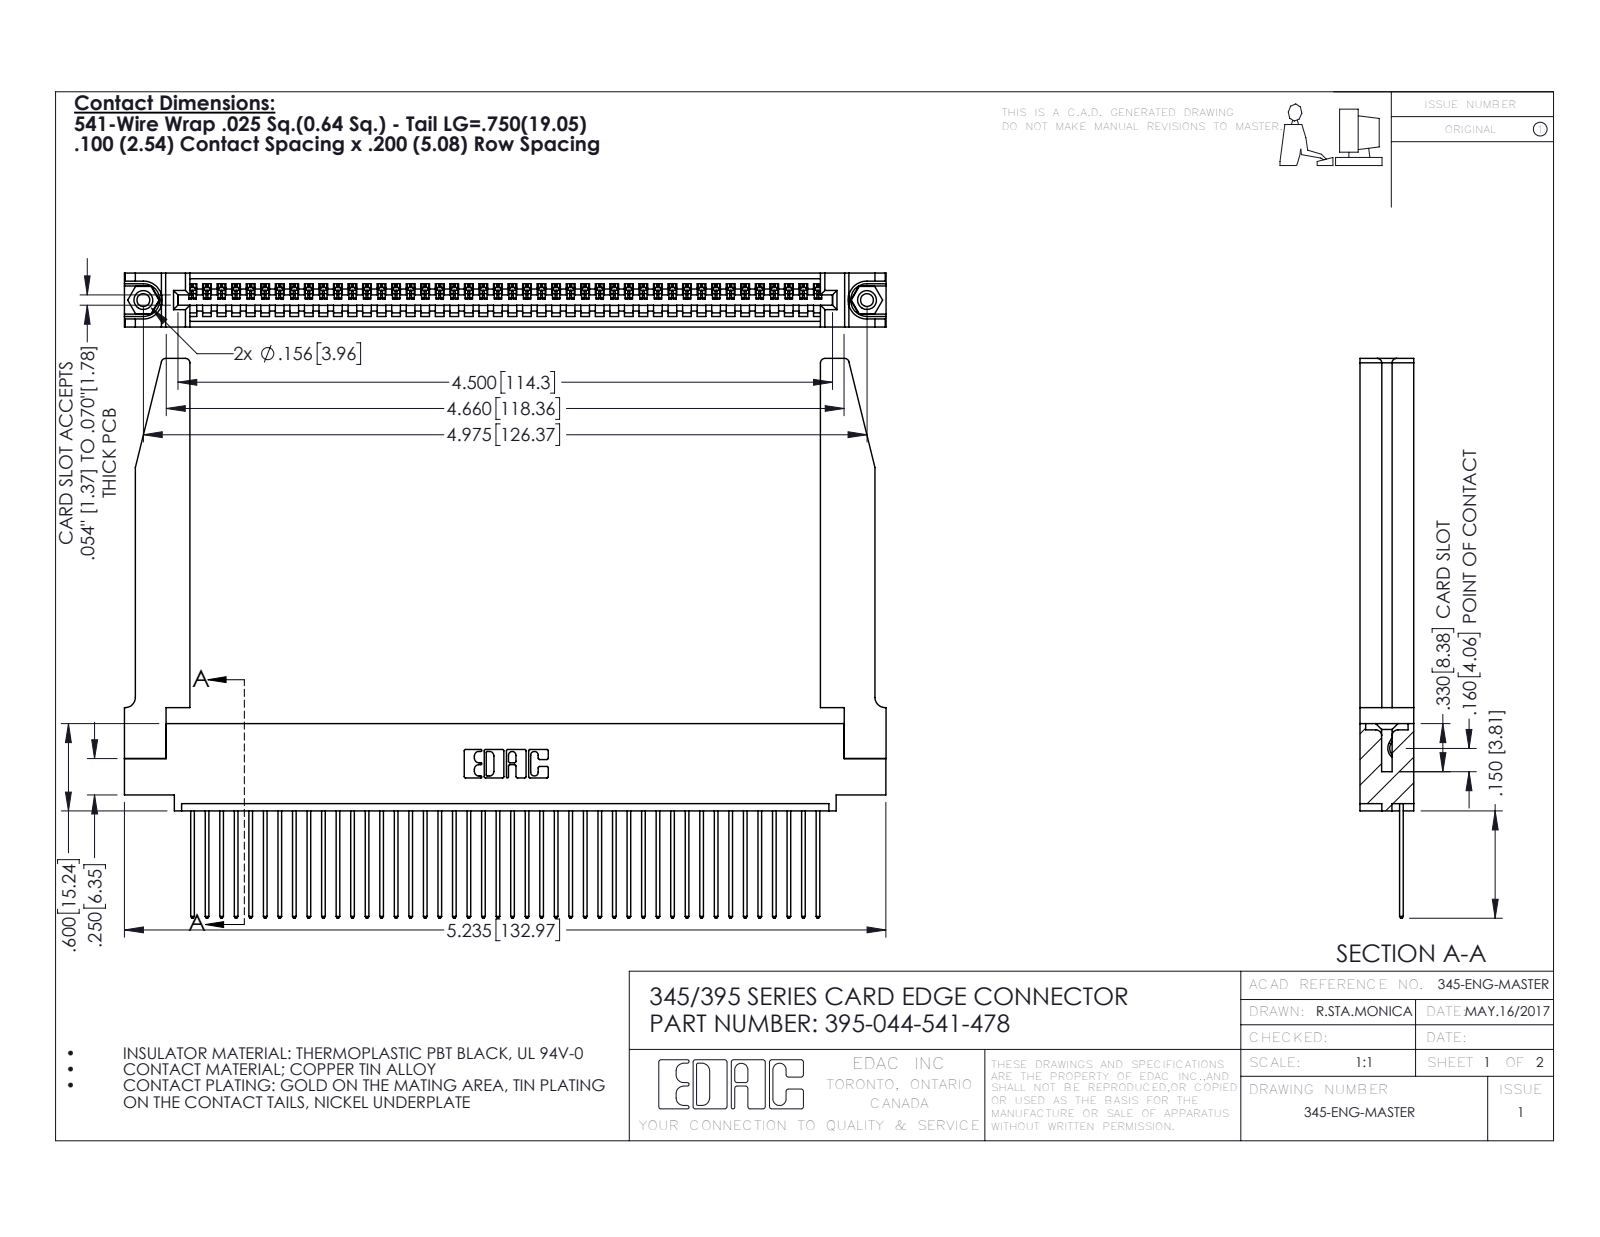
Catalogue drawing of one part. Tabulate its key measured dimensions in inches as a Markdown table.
| quantity | value |
| --- | --- |
| part name | 345-292-001_345-293-141; 395-044-541-478; 345-220-078_345-220-078; 345-250-001_345-250-001-102 (+1 more) |
| STEP written by | SolidWorks 2016 (CONFIG_CONTROL_DESIGN) |
| units | inches |
| bodies | 49 solids, 2916 faces (1986 planar, 878 cylindrical, 52 other) |
| overall size | 5.236 × 3.847 × 0.37 |
| volume | 1.25 in³ |
| surface area | 38.31 in² |
| round holes (diameter × count) | 0.089 × 2, 0.125 × 2, 0.156 × 2, 0.064 × 1 |
| round bosses / shafts (diameter × count) | 0.155 × 2 |
| partial cylindrical surfaces (radius × count) | 0.006 × 88, 0.01 × 88, 0.01 × 22, 0.03 × 8, 0.007 × 6, 0.031 × 6, 0.026 × 3, 0.031 × 2 |
| main face-to-face distances | 0.072, 0.37, 0.298, 0.098, 0.272, 0.025, 0.2, 0.225, 0.148, 0.15 |
| hole center spacings | 0.27, 4.739, 4.975 |
